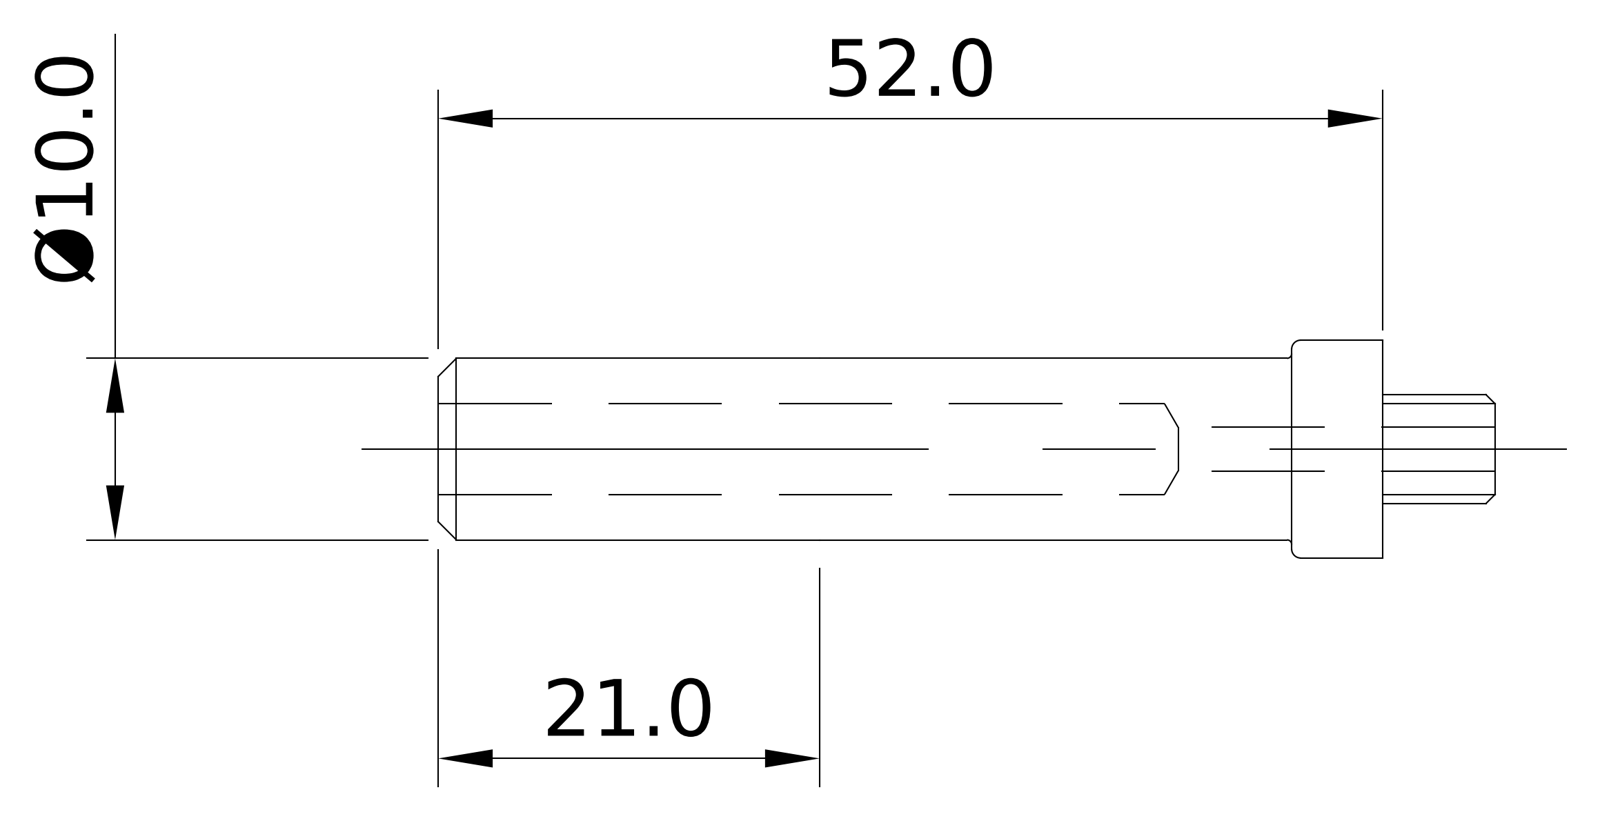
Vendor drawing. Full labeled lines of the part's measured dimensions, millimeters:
STEP written by: ACIS (automotive_design)
Units: millimetres
Bodies: 1 solid, 22 faces (4 planar, 10 cylindrical, 8 other)
Overall size (bounding box): 58 × 12 × 12
Volume: 3 510 mm³ · Surface area: 2 727 mm²
Round holes (diameter × count): ⌀2 ×1, ⌀5 ×1
Round bosses / shafts (diameter × count): ⌀12 ×1, ⌀10 ×1, ⌀6 ×1
Main face-to-face distances: 52, 5, 47, 6, 11, 58
